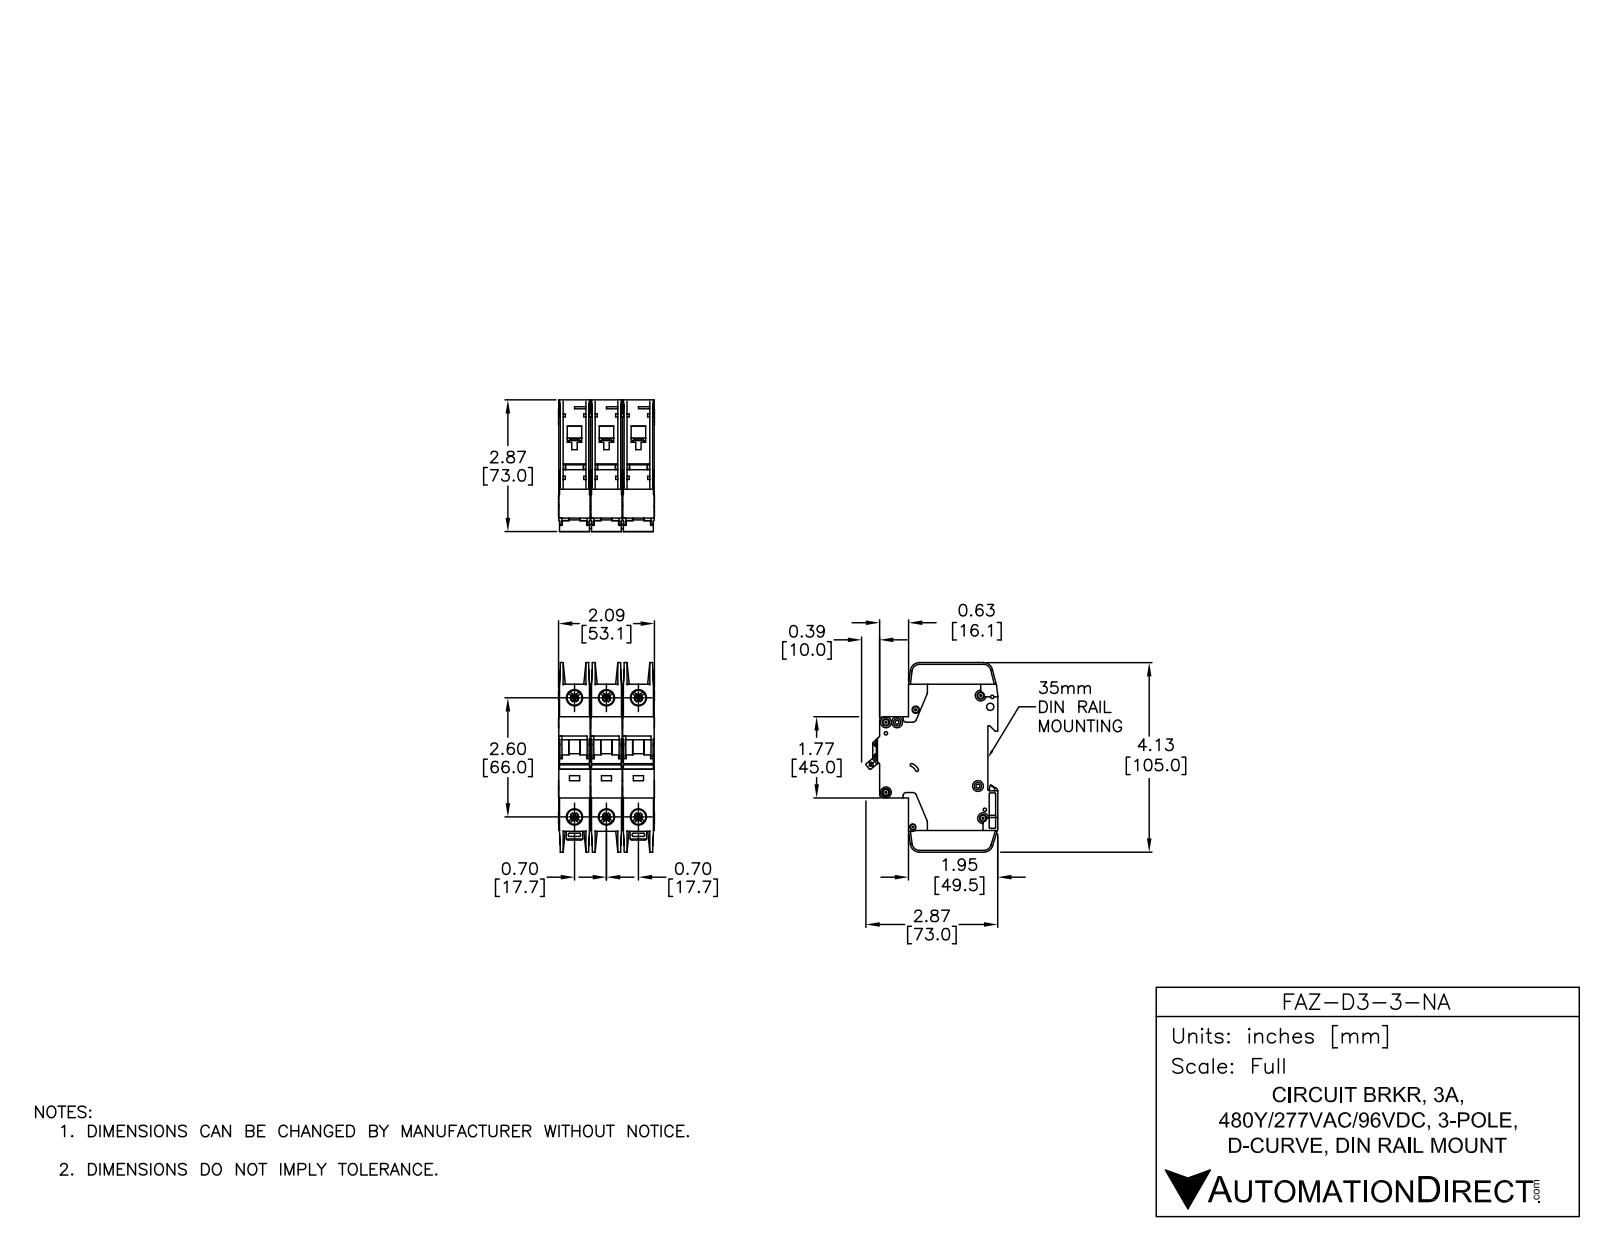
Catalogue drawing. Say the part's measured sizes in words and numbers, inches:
The part is named "FAZ-D3-3-NA". Its 3-D file was written by "SolidWorks 2014 (AUTOMOTIVE_DESIGN)". It is 9 solids with 2352 faces: 1227 planar, 789 cylindrical and 336 other. Overall it measures 4.134 by 2.876 by 2.091 inches. Its volume is 14.22 cubic inches and its surface area 115 square inches. Round holes: 7 of diameter 0.142, 6 of diameter 0.281, 6 of diameter 0.323, 2 of diameter 0.043, 2 of diameter 0.059, 2 of diameter 0.157, 1 of diameter 0.075, 1 of diameter 0.085, 1 of diameter 0.087, 1 of diameter 0.1, 1 of diameter 0.13, 1 of diameter 0.134. Round bosses or shafts: 7 of diameter 0.236, 3 of diameter 0.098. Partial cylindrical surfaces (rounded edges, fillets, slot ends): 65 of radius 0.01, 30 of radius 0.02, 26 of radius 0.039, 14 of radius 0.079, 5 of radius 0.071, 5 of radius 0.197, 4 of radius 0.157, 2 of radius 0.008. The main face-to-face distances are 0.697, 1.394, 0.689, 1.386, 0.028, 0.593, 0.096, 0.069, 0.62, 0.524. The hole center spacings are 0.697, 2.69, 2.598, 0.244, 1.394, 2.948, 0.204, 0.24.
